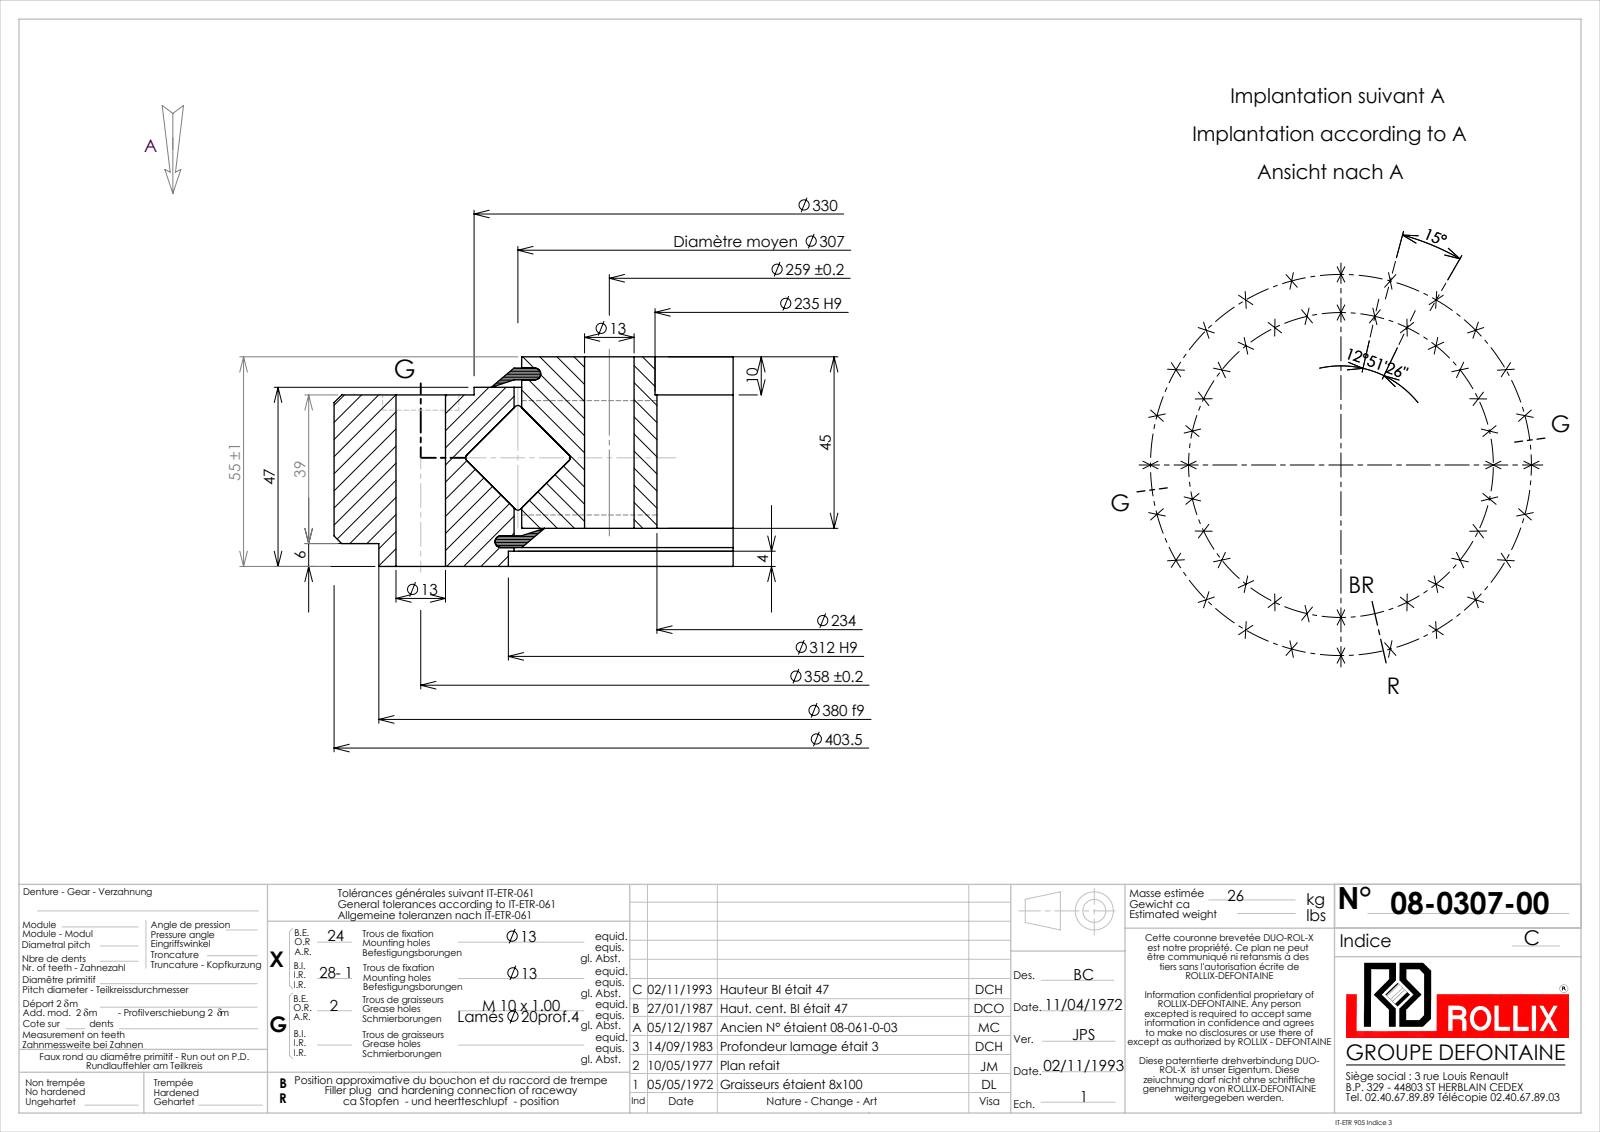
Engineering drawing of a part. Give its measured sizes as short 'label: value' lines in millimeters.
name: 08-0307-00
written by: SolidWorks 2016 (CONFIG_CONTROL_DESIGN)
unit: mm
bodies: 5 solids, 202 faces (20 planar, 136 cylindrical, 46 other)
size: 403.5 × 403.5 × 55
volume: 3 046 000 mm³; area: 521 411 mm²
holes: 51× ⌀13, 2× ⌀9, 2× ⌀20, 1× ⌀234, 1× ⌀235, 1× ⌀309, 1× ⌀312
bosses: 1× ⌀403.5, 1× ⌀380, 1× ⌀330, 1× ⌀305, 1× ⌀20
face distances: 45, 10, 35, 55, 1.95, 38.95, 5.05, 42.05, 3.1, 44
hole spacings: 179, 46.73, 137, 284.02, 330.75, 345.8, 354.94, 92.66
